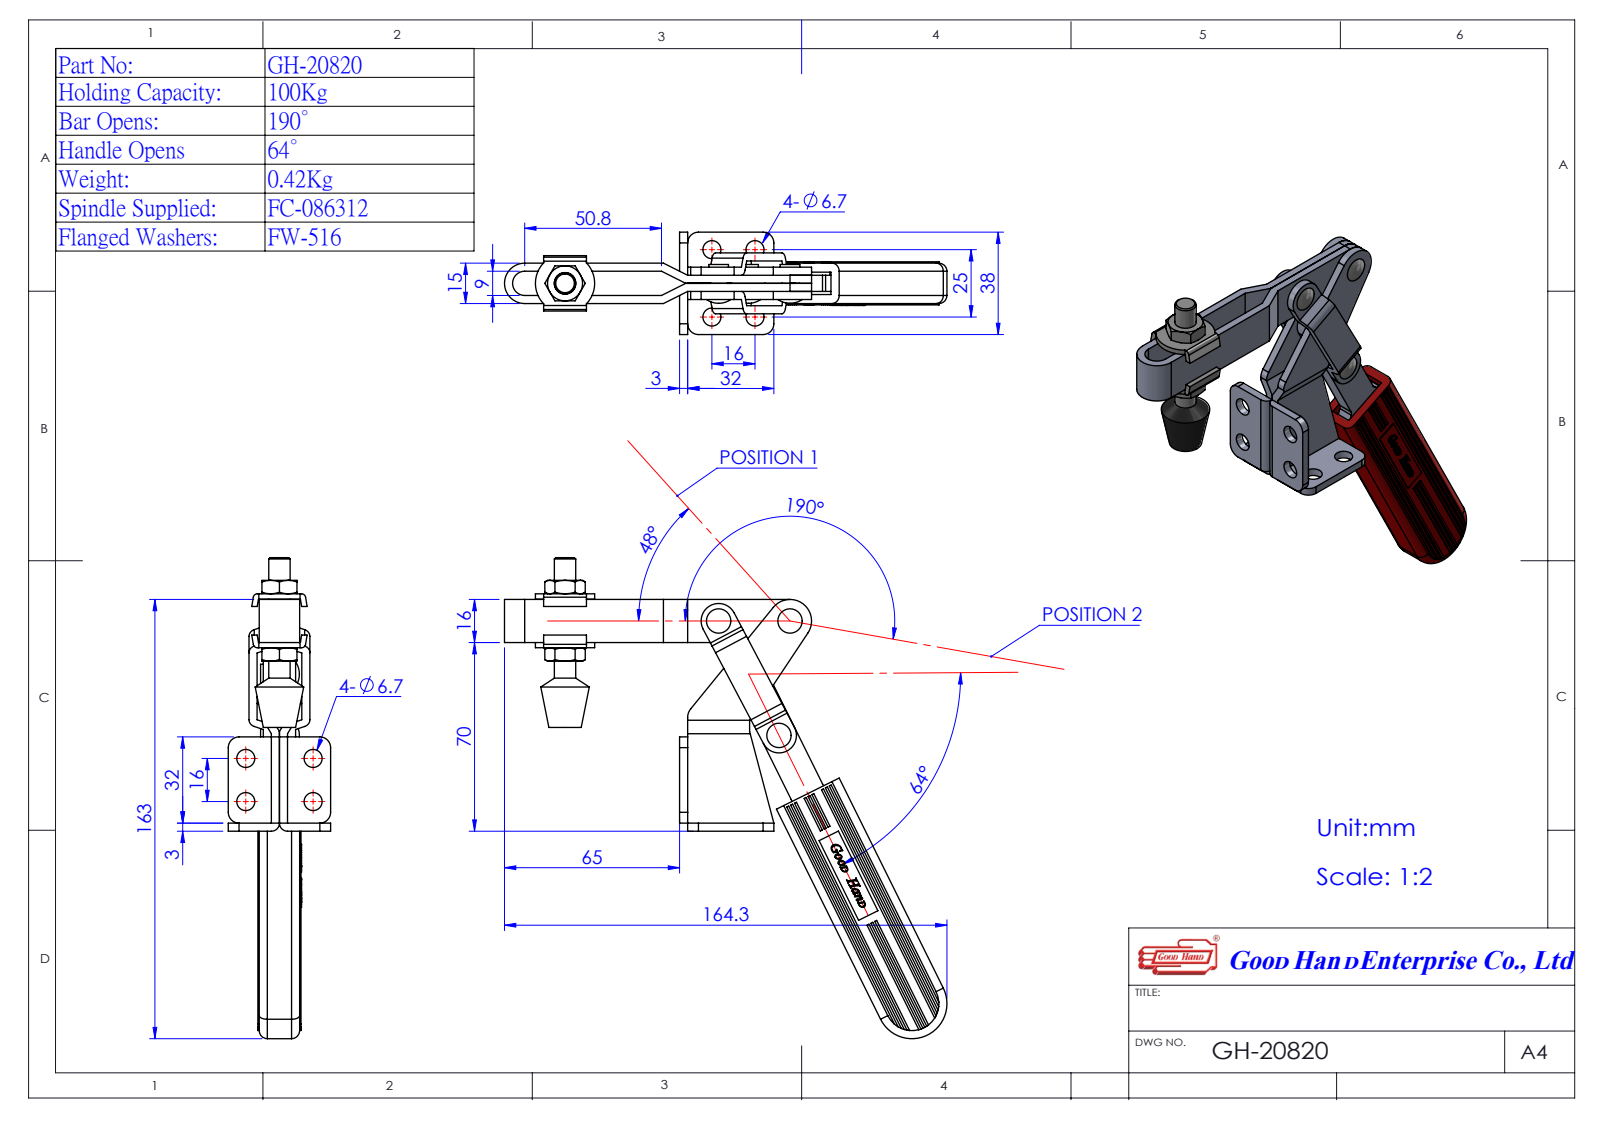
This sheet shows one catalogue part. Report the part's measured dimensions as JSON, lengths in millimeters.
{"part_name": "Group1^GH-20820(簡化); Group4^GH-20820(簡化); GH-20820(簡化); Group2^GH-20820(簡化) (+2 more)", "step_written_by": "SolidWorks 2016 (AUTOMOTIVE_DESIGN)", "units": "millimeters", "bodies": {"solids": 5, "faces": 264, "planar": 135, "cylindrical": 89, "other": 40}, "overall_size": [178.49, 164.26, 38], "volume_mm3": 84829, "surface_area_mm2": 40992, "round_holes": [[6.7, 8], [5, 4], [4.4, 1]], "round_bosses_or_shafts": [[7.3, 4], [7.93, 1]], "partial_cylinders_radius": [[4, 6], [1.5, 4], [6.5, 3], [2, 2], [4.02, 2], [4.5, 1], [5, 1], [7.5, 1]], "face_to_face_distances": [3, 4.5, 10.5, 6, 1.5, 7.5, 15, 9, 12, 13.5], "hole_center_spacings": [25, 16, 29.68, 22.62, 25.41, 26.5, 42.66, 48.01]}
